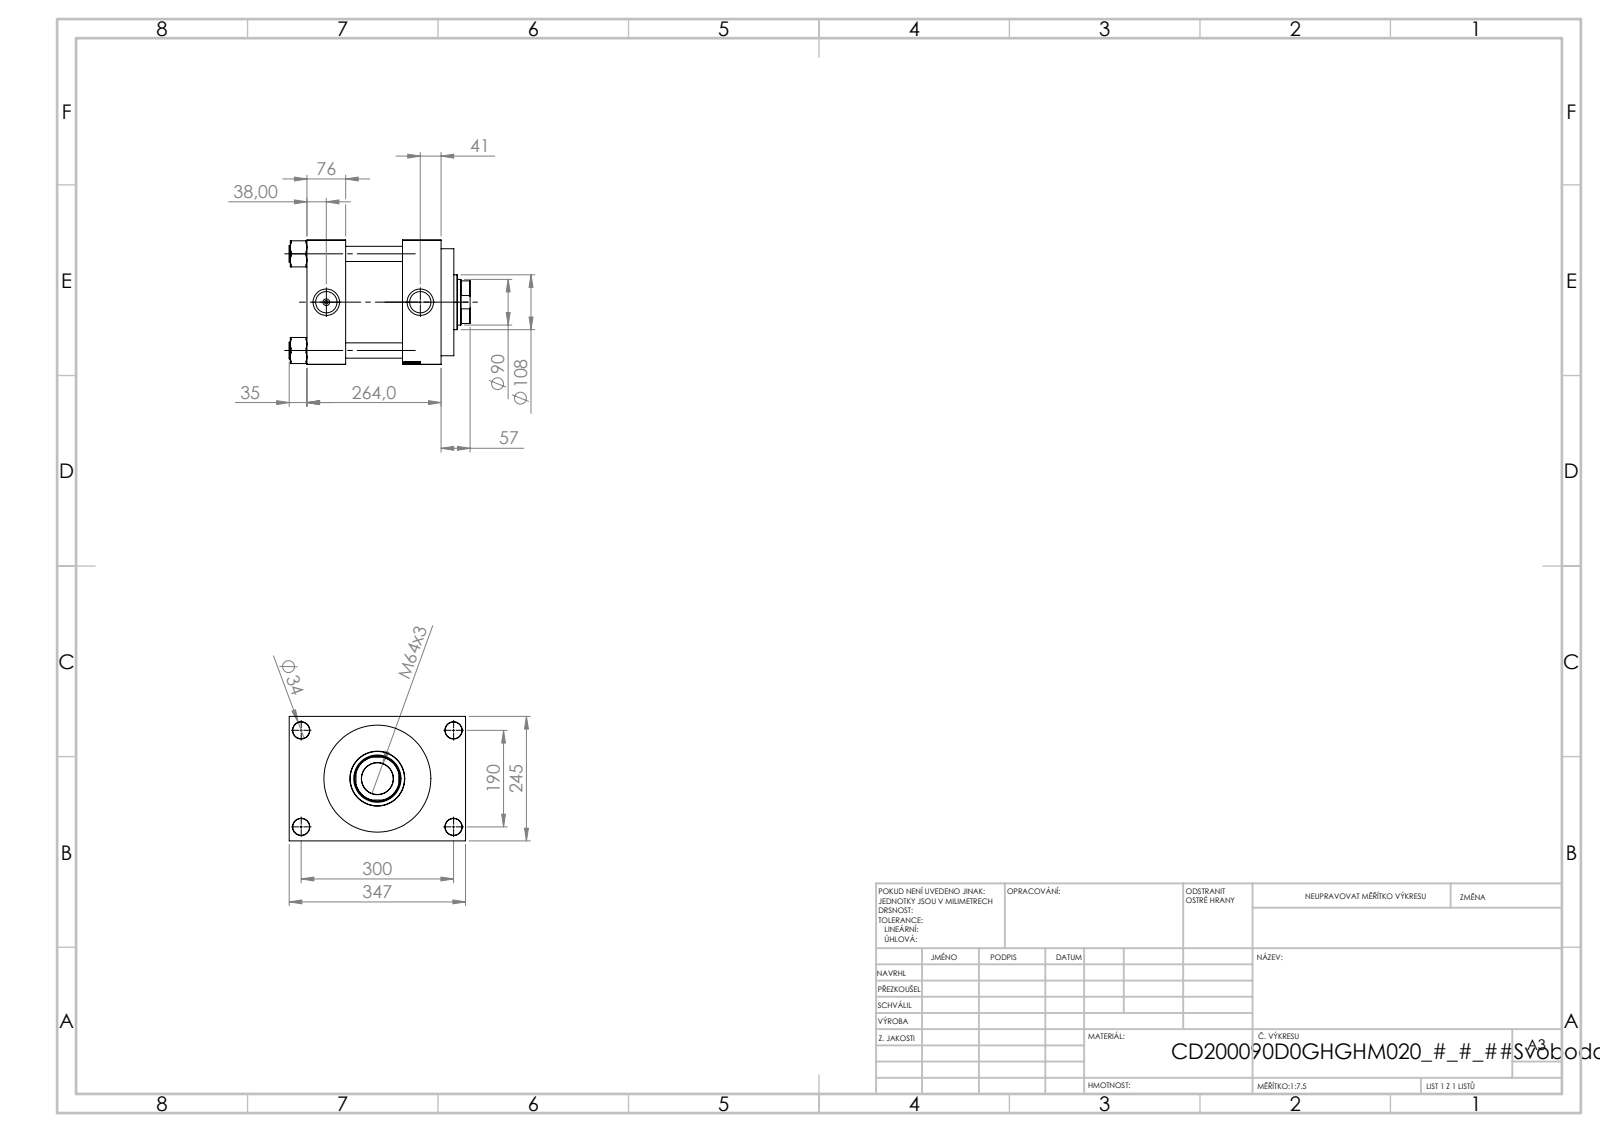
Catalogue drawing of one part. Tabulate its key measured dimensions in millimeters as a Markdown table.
| quantity | value |
| --- | --- |
| part name | V215CD_NUT_M5_D; V215CD_VCP_D; V215CD_D_TYCINKA; V215CD_D_Body (+1 more) |
| STEP written by | SolidWorks 2019 (CONFIG_CONTROL_DESIGN) |
| units | millimeters |
| bodies | 11 solids, 1148 faces (544 planar, 86 cylindrical, 518 other) |
| overall size | 356 × 347 × 245 |
| volume | 14 650 000 mm³ |
| surface area | 1 097 000 mm² |
| round holes (diameter × count) | 30 × 4, 33 × 4, 7 × 2, 41.92 × 2, 52 × 2, 62.5 × 1, 90 × 1, 93 × 1, 146 × 1, 200 × 1, 210.5 × 1 |
| round bosses / shafts (diameter × count) | 33 × 4, 206 × 1, 108 × 1 |
| partial cylindrical surfaces (radius × count) | 44 × 1 |
| main face-to-face distances | 76, 188, 245, 112, 264, 245.74, 169.74, 57.74, 18.26, 51 |
| hole center spacings | 54.9, 134.49, 177.55, 190.2, 197.87, 245.1, 310.18, 190 |
